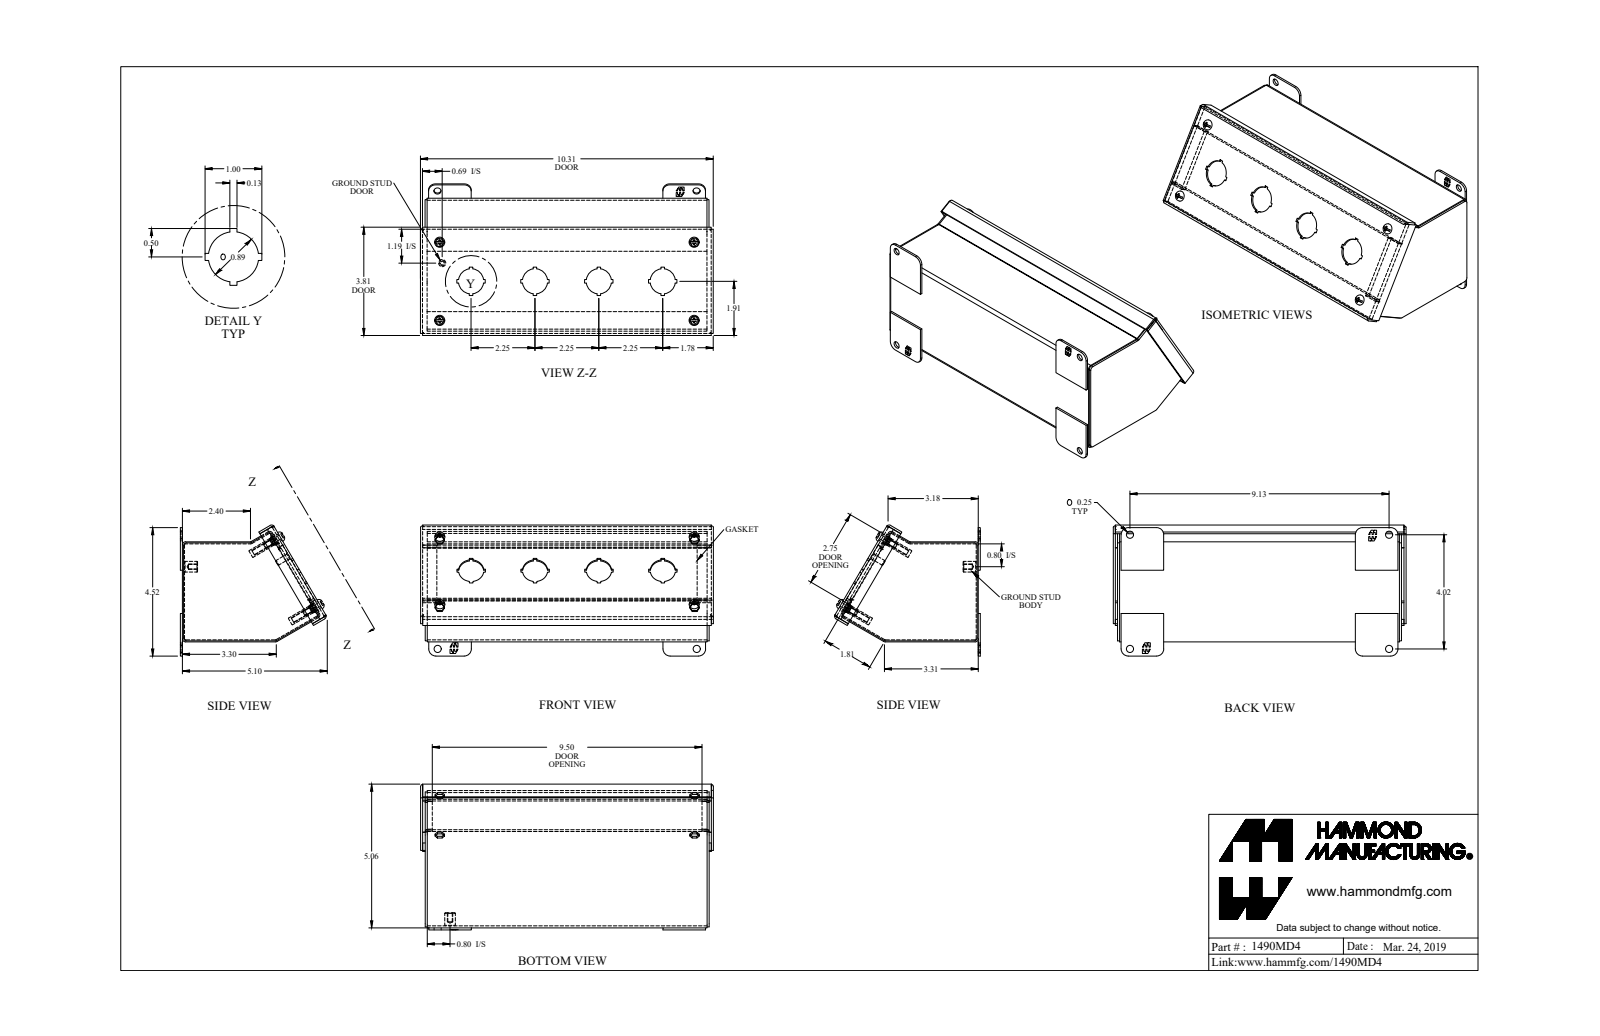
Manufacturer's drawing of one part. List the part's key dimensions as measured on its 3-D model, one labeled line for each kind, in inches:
Part name (STEP PRODUCT): 1490MD4_Default
STEP written by: SolidWorks 2019 (CONFIG_CONTROL_DESIGN)
Units: inches
Bodies: 21 solids, 660 faces (466 planar, 156 cylindrical, 38 other)
Overall size (bounding box): 10.312 × 5.176 × 4.635
Volume: 15.64 in³ · Surface area: 448.1 in²
Round holes (diameter × count): ⌀0.25 ×8, ⌀0.159 ×4, ⌀0.875 ×2, ⌀0.875 ×2, ⌀0.156 ×1
Round bosses / shafts (diameter × count): ⌀0.39 ×4, ⌀0.275 ×4, ⌀0.19 ×4, ⌀0.148 ×4, ⌀0.375 ×1
Partial cylindrical surfaces — rounded edges, fillets, slot ends (radius × count): R0.108 ×18, R0.036 ×12, R0.25 ×8, R0.125 ×4, R0.16 ×4, R0.171 ×4
Main face-to-face distances: 0.072, 3.45, 9.928, 3.522, 3.378, 9.856, 10, 3.428, 0.221, 0.223
Hole centre spacings: 8.96, 8.974, 1.764, 2.25, 0.016, 2.744, 2.75, 2.751
